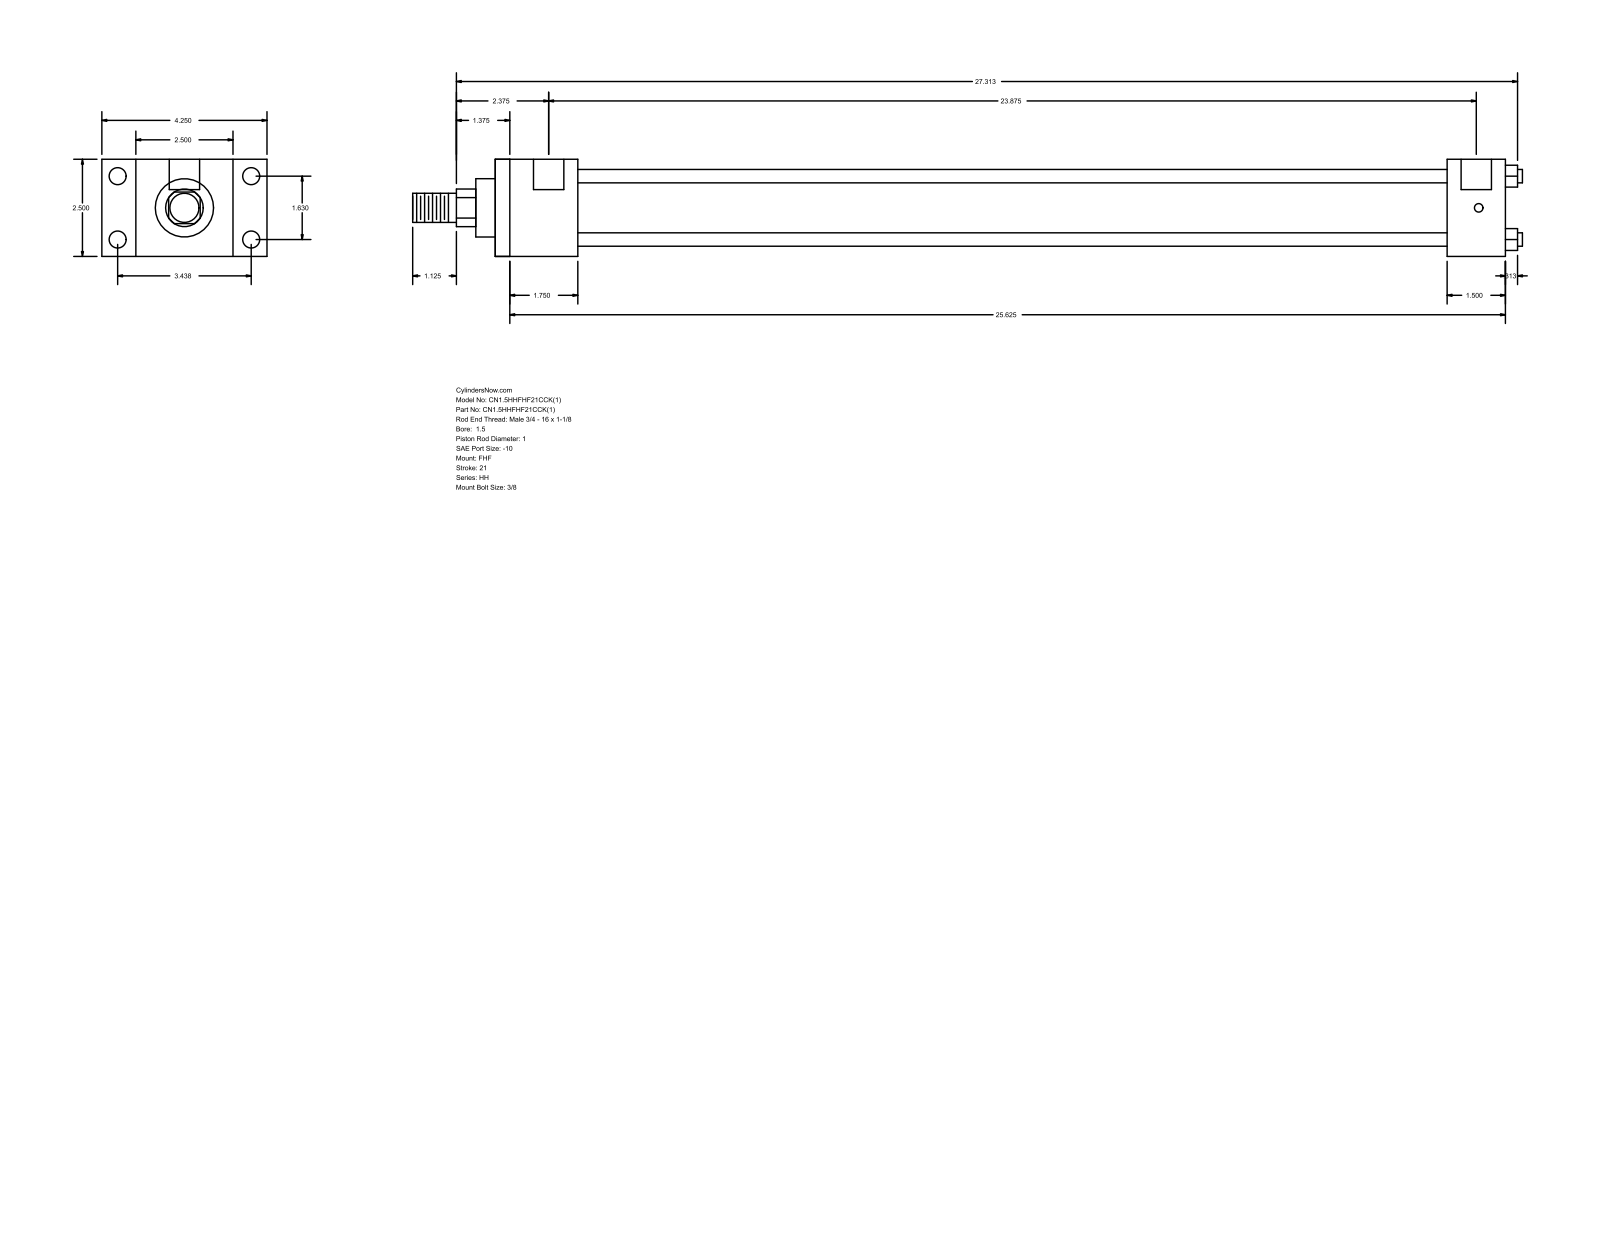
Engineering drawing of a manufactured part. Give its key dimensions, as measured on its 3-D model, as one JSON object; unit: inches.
{"part_name": "HH_FHF__0150_1", "step_written_by": "GSSL Pune (CONFIG_CONTROL_DESIGN)", "units": "inches", "bodies": {"solids": 0, "faces": 88, "planar": 60, "cylindrical": 28, "other": 0}, "overall_size": [28.563, 4.25, 2.5], "round_holes": [[0.219, 4], [0.438, 4], [0.781, 2]], "round_bosses_or_shafts": [[0.345, 4], [1.75, 1], [1.5, 1], [1, 1], [0.75, 1]], "partial_cylinders_radius": [[0.484, 1]], "face_to_face_distances": [2.5, 0.875, 3.375, 2.125, 4.25, 26, 23.875, 1.5, 24.5, 22.375], "hole_center_spacings": [0.063, 1.63, 3.438, 3.805, 23.937, 24, 23.875]}
